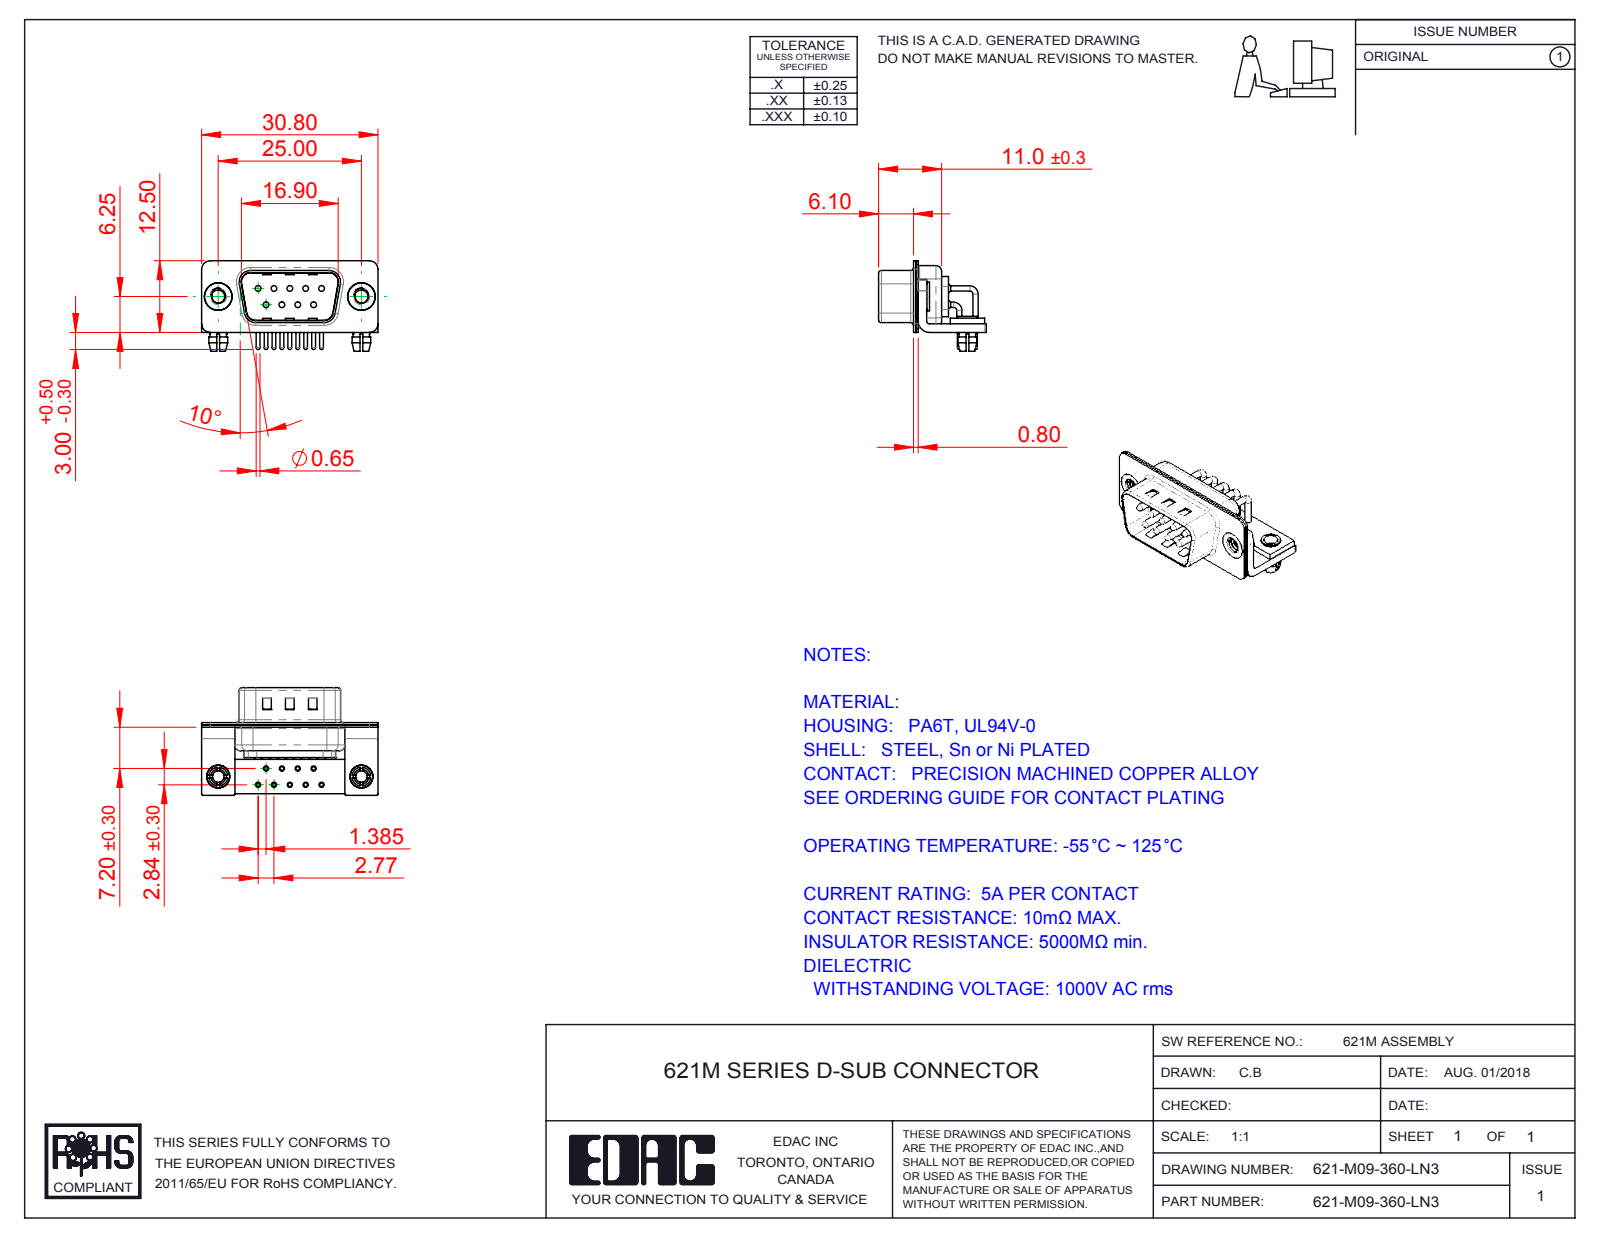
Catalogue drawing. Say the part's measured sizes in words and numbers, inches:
The part is named "621M Contact Row 1; 621M Stabilizer Bracket; 621M Contact Row 2; 621M Shell Rear_09 Contacts (+6 more)". Its 3-D file was written by "SolidWorks 2016 (CONFIG_CONTROL_DESIGN)". It is 19 solids with 1454 faces: 757 planar, 525 cylindrical and 172 other. Overall it measures 1.213 by 0.74 by 0.622 inches. Its volume is 0.11 cubic inches and its surface area 7.835 square inches. Round holes: 11 of diameter 0.079, 9 of diameter 0.035, 9 of diameter 0.039, 9 of diameter 0.067, 2 of diameter 0.089, 2 of diameter 0.098, 2 of diameter 0.126, 2 of diameter 0.157, 2 of diameter 0.189. Round bosses or shafts: 9 of diameter 0.059, 9 of diameter 0.035, 9 of diameter 0.026, 2 of diameter 0.197, 2 of diameter 0.193, 2 of diameter 0.157, 2 of diameter 0.134, 2 of diameter 0.13. Partial cylindrical surfaces (rounded edges, fillets, slot ends): 16 of radius 0.01, 16 of radius 0.059, 13 of radius 0.079, 9 of radius 0.02, 9 of radius 0.04, 8 of radius 0.063, 4 of radius 0.024, 4 of radius 0.026. The main face-to-face distances are 0.016, 0.059, 0.031, 0.033, 0.049, 0.039, 0.409, 0.376, 0.098, 0.075. The hole center spacings are 0.124, 0.109, 0.218, 0.198, 0.198, 0.327, 0.294, 0.295.
